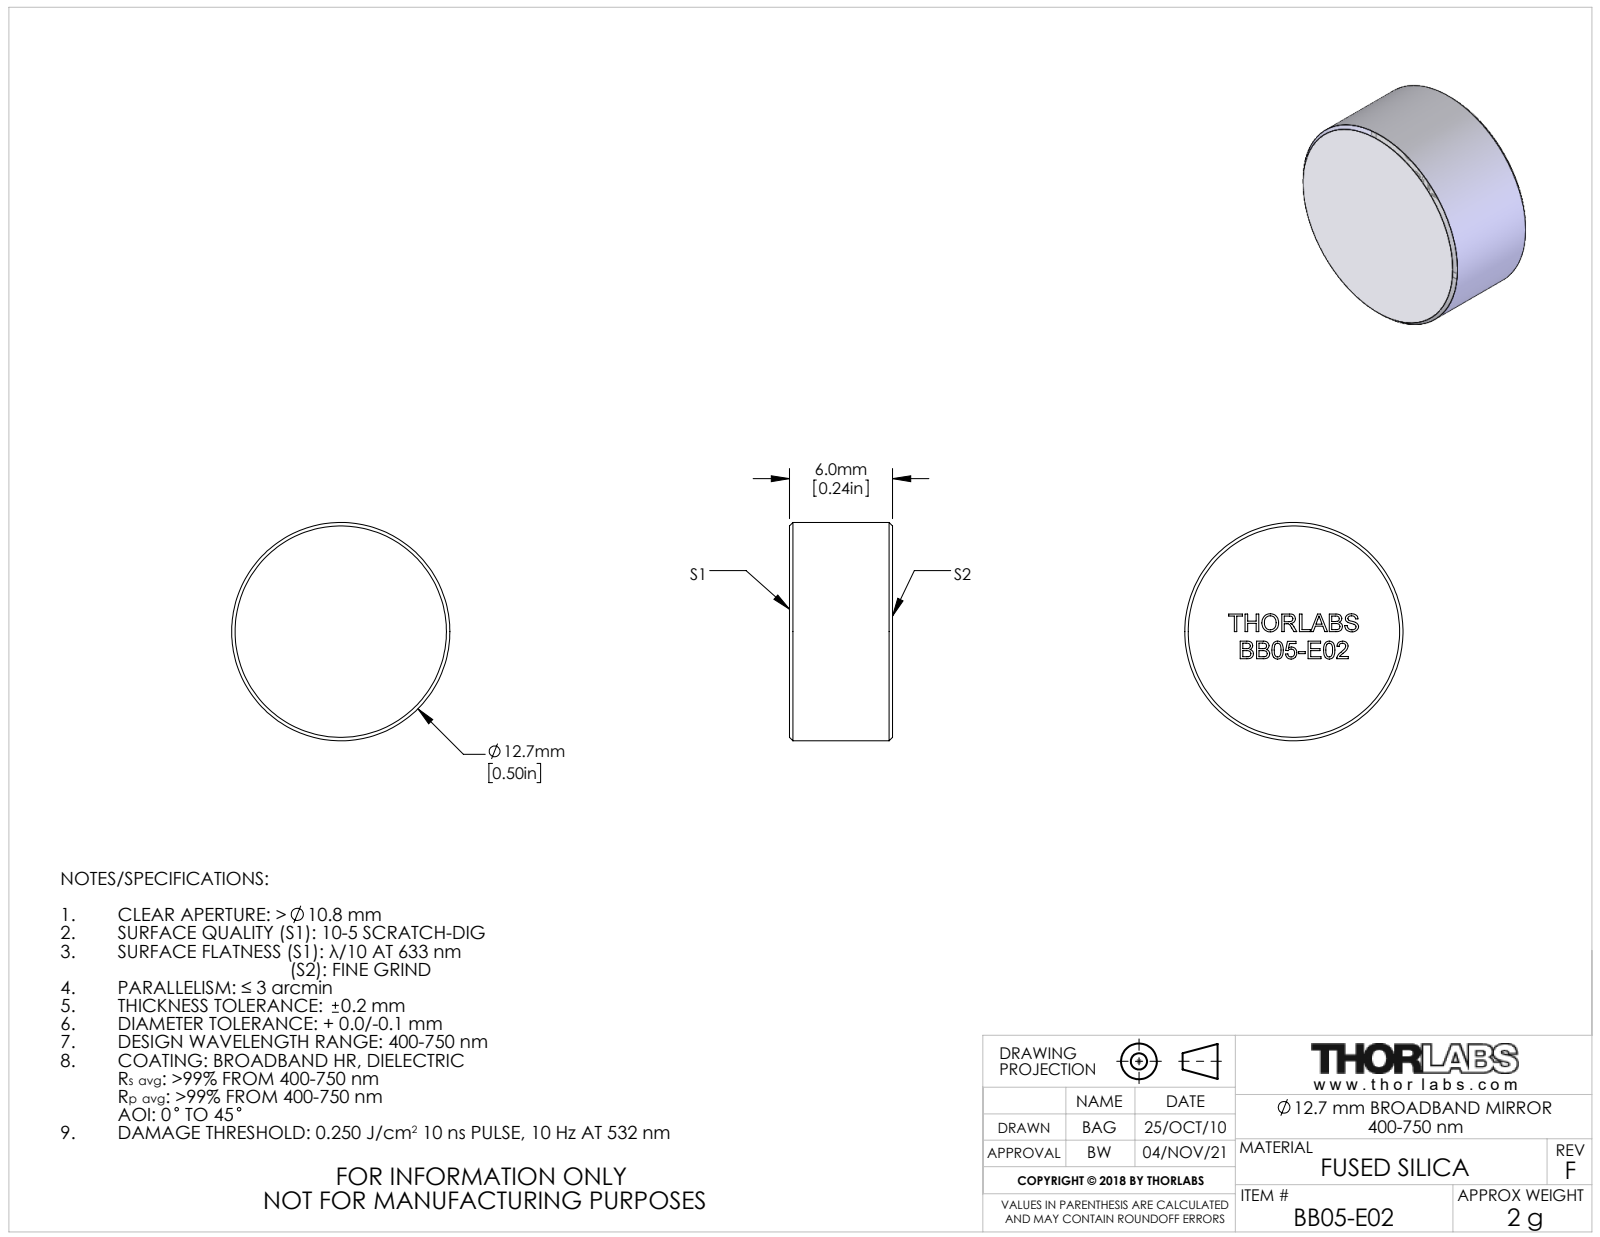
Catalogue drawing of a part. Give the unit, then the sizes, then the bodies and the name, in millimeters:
Units: millimetres
Overall size (bounding box): 12.7 × 12.7 × 6
Round bosses / shafts (diameter × count): ⌀12.7 ×1
Main face-to-face distances: 6, 1.6, 1, 0.9, 0.8, 1.6, 0.5, 2.5, 0.7, 1.3
Volume: 750 mm³ · Surface area: 483 mm²
Bodies: 1 solid, 239 faces (133 planar, 2 cylindrical, 104 other)
Part name (STEP PRODUCT): 3540-E0W
STEP written by: SolidWorks 2016 (CONFIG_CONTROL_DESIGN)
